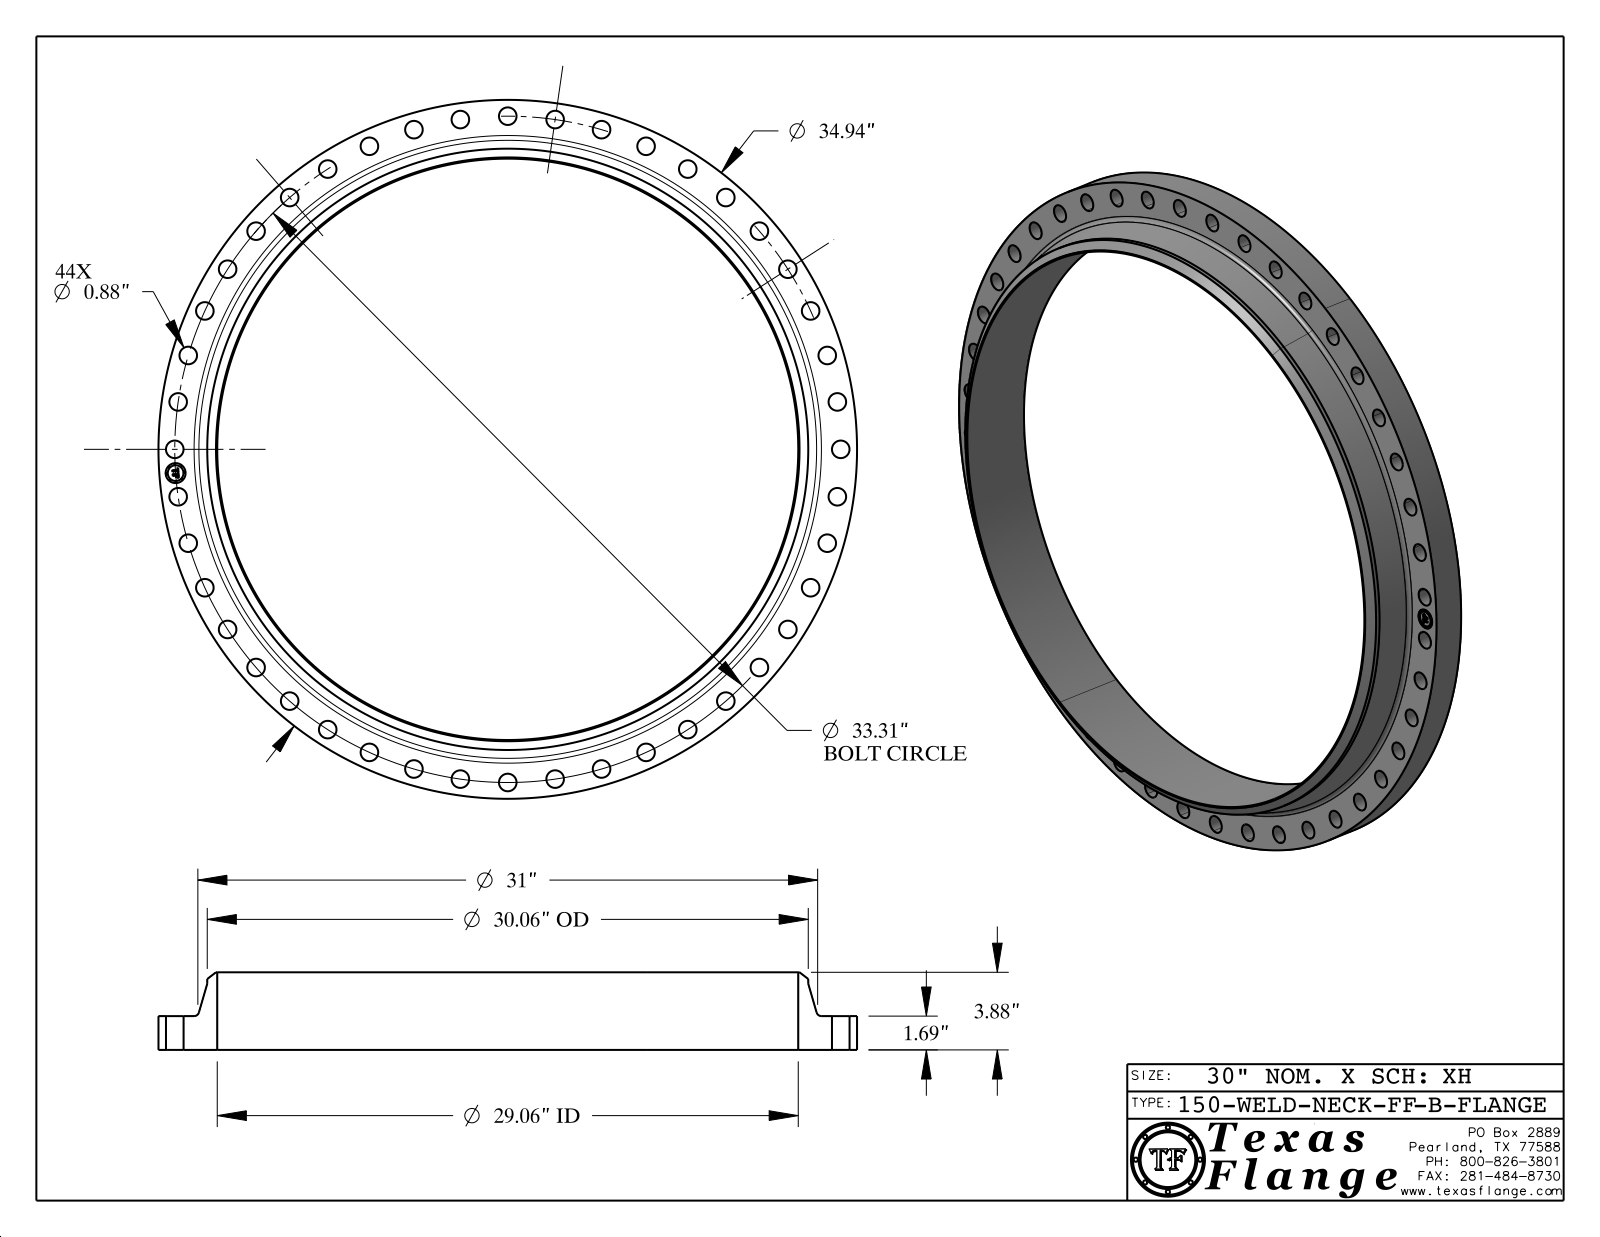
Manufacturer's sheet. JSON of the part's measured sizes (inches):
{"part_name": "150-WELD-NECK-FF, Series B", "step_written_by": "CATIA V5 STEP AP214 (AUTOMOTIVE_DESIGN)", "units": "inches", "bodies": {"solids": 1, "faces": 488, "planar": 368, "cylindrical": 114, "other": 6}, "overall_size": [34.94, 34.94, 3.88], "volume_in3": 586, "surface_area_in2": 1427, "round_holes": [[0.88, 44], [1, 1], [29.06, 1]], "round_bosses_or_shafts": [[0.061, 8], [34.94, 1], [30.06, 1], [0.788, 1]], "face_to_face_distances": [1.69, 3.88, 2.19, 0.015, 1.675, 2.205, 0.298, 0.292, 0.054, 0.193], "hole_center_spacings": [16.655, 2.376, 33.225, 31.961, 32.971, 32.549, 4.741, 11.641]}
